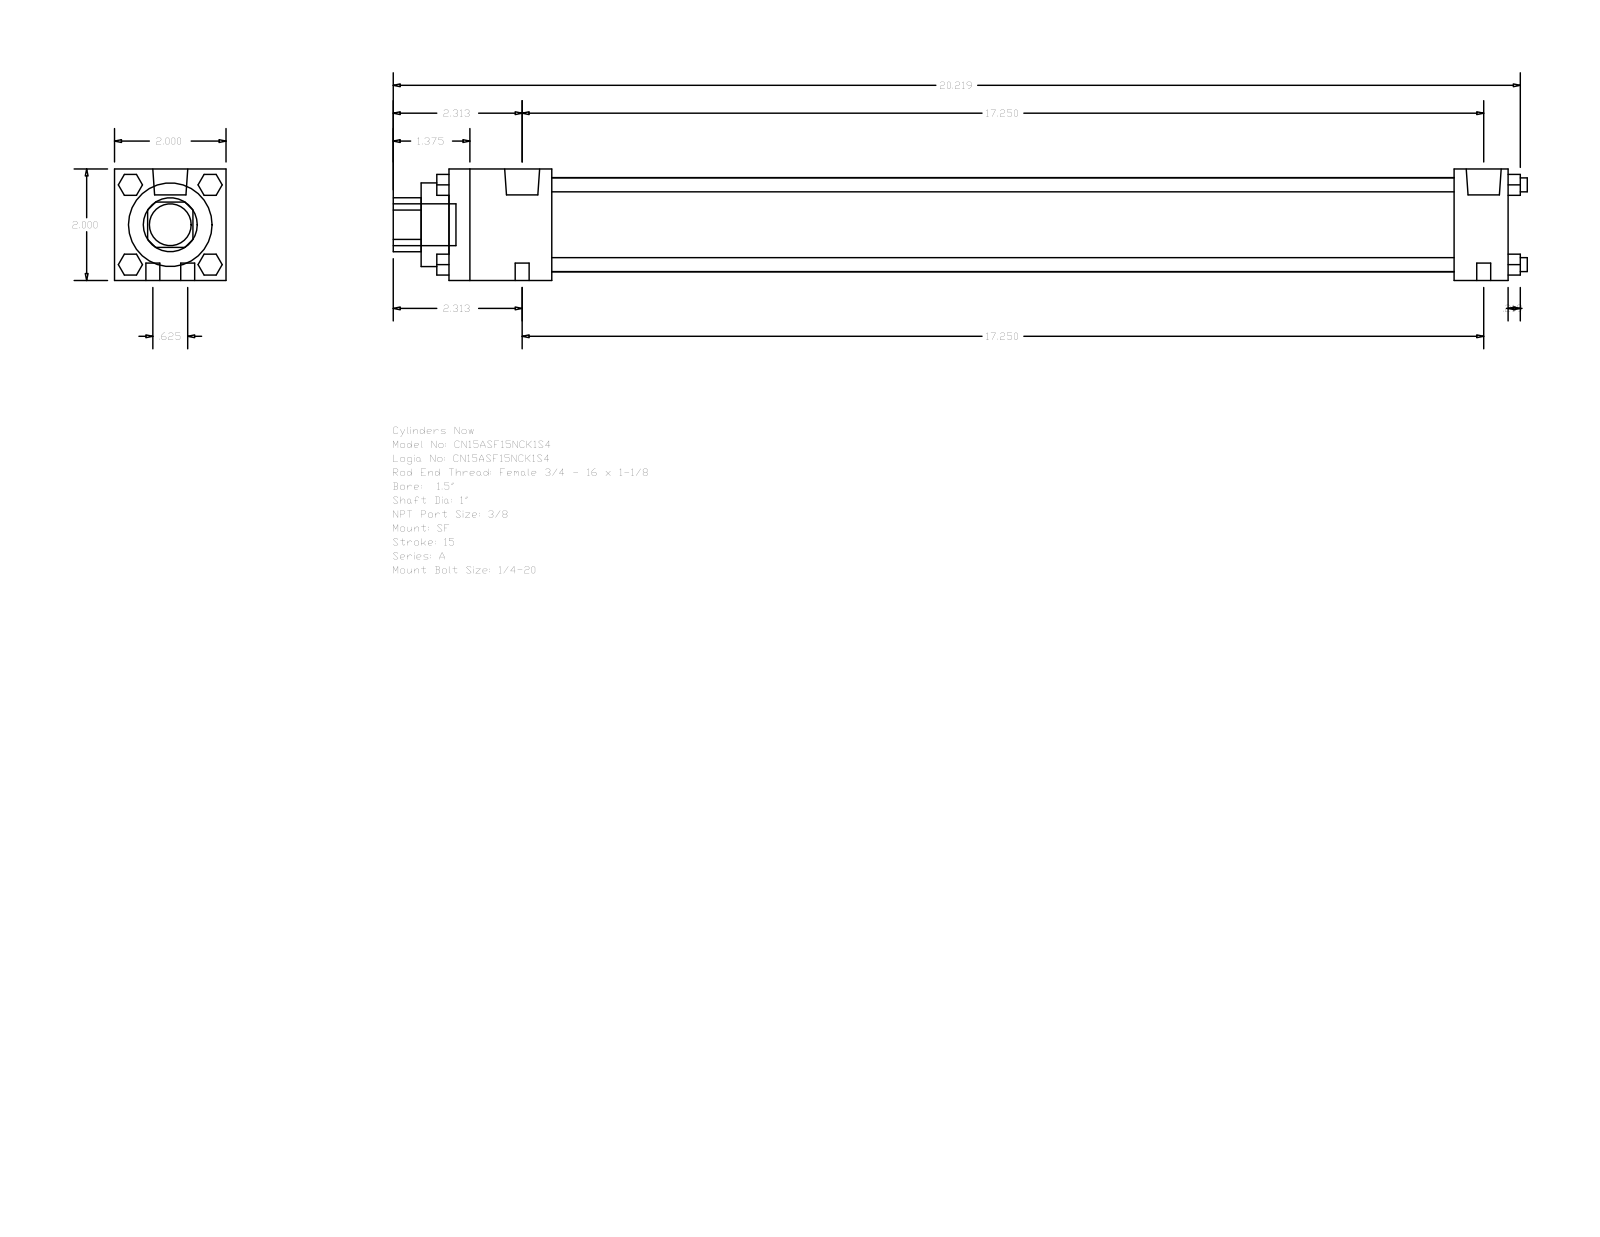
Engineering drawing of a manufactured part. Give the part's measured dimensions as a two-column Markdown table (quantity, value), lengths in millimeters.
| quantity | value |
| --- | --- |
| part name | A_SF__0150_1 |
| STEP written by | GSSL Pune (CONFIG_CONTROL_DESIGN) |
| units | millimeters |
| bodies | 0 solids, 124 faces (94 planar, 30 cylindrical, 0 other) |
| overall size | 516.73 × 50.8 × 50.8 |
| round holes (diameter × count) | 25.4 × 1, 38.1 × 1, 42.93 × 1 |
| round bosses / shafts (diameter × count) | 6.35 × 8, 15.93 × 2, 5.56 × 2, 19.05 × 1 |
| partial cylindrical surfaces (radius × count) | 12.29 × 1 |
| main face-to-face distances | 50.8, 482.6, 46.83, 457.99, 411.16, 435.77, 24.61, 12.7, 59.53, 470.69 |
